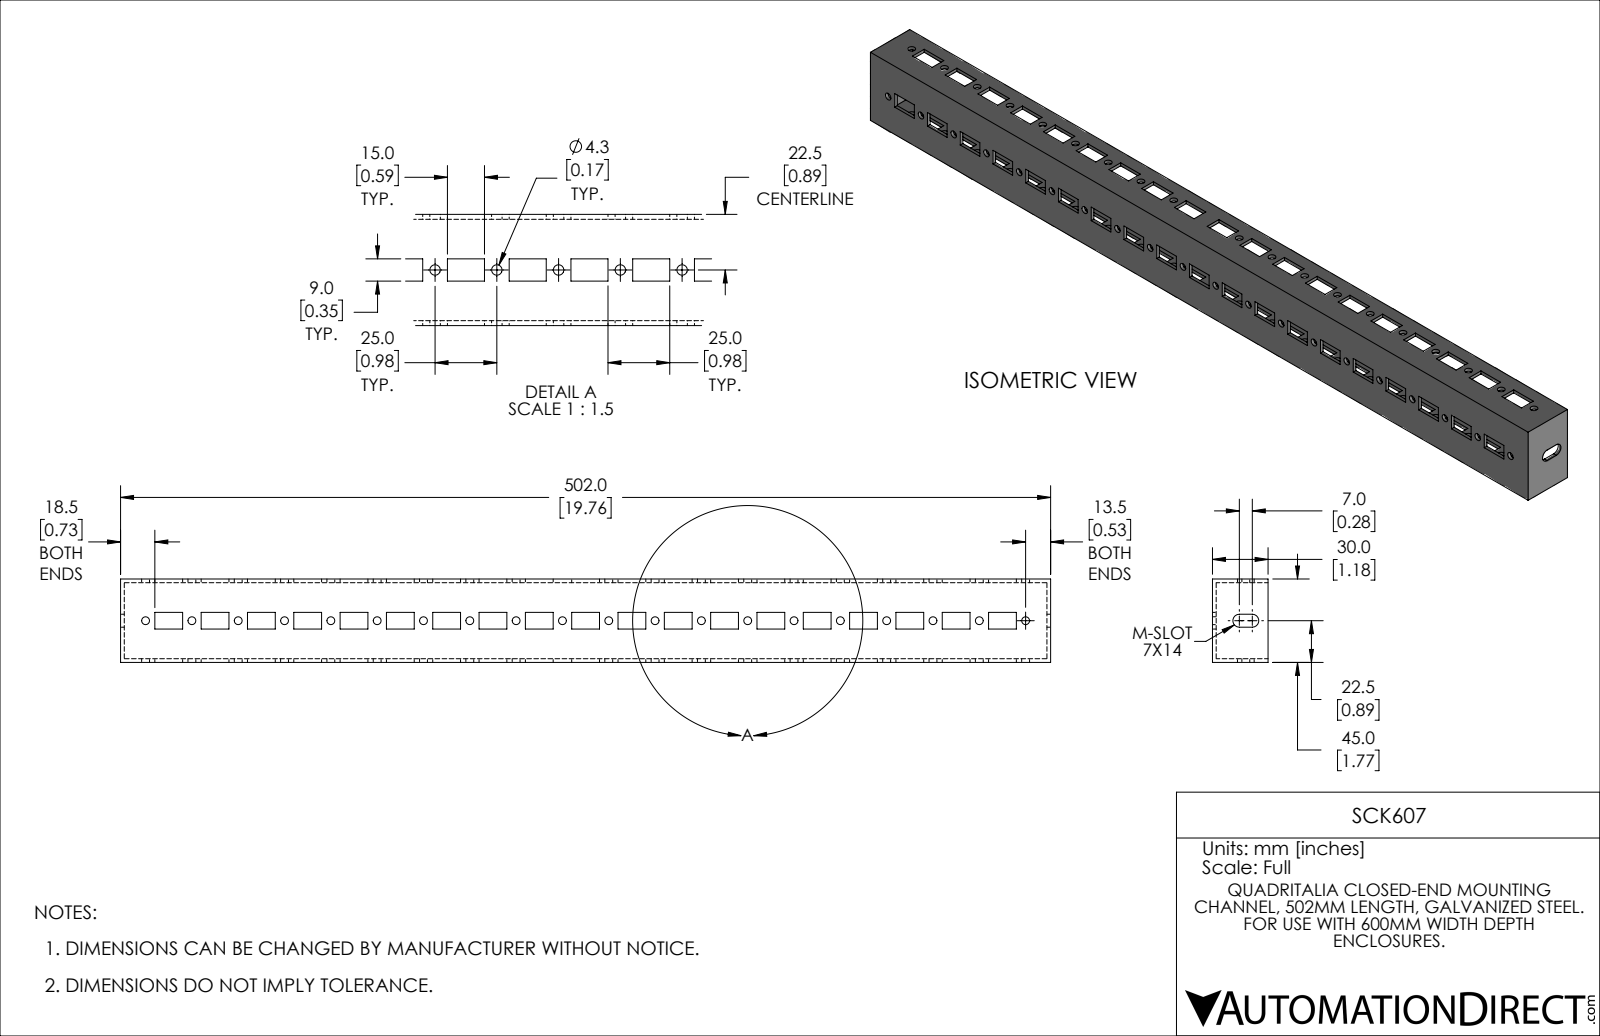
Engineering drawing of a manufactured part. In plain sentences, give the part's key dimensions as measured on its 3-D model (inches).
The part is named "SCK607". Its 3-D file was written by "SolidWorks 2021 (CONFIG_CONTROL_DESIGN)". It is 1 solid with 305 faces: 243 planar, 62 cylindrical and 0 other. Overall it measures 19.764 by 1.772 by 1.181 inches. Its volume is 5.407 cubic inches and its surface area 151.8 square inches. Round holes: 39 of diameter 0.167. Partial cylindrical surfaces (rounded edges, fillets, slot ends): 2 of radius 0.138. The main face-to-face distances are 0.079, 1.693, 1.772, 1.614, 1.181, 1.102, 19.685, 0.984, 0.354, 19.764. The hole center spacings are 0.984, 1.969, 2.953, 3.937, 4.921, 5.906, 6.89, 7.874.
